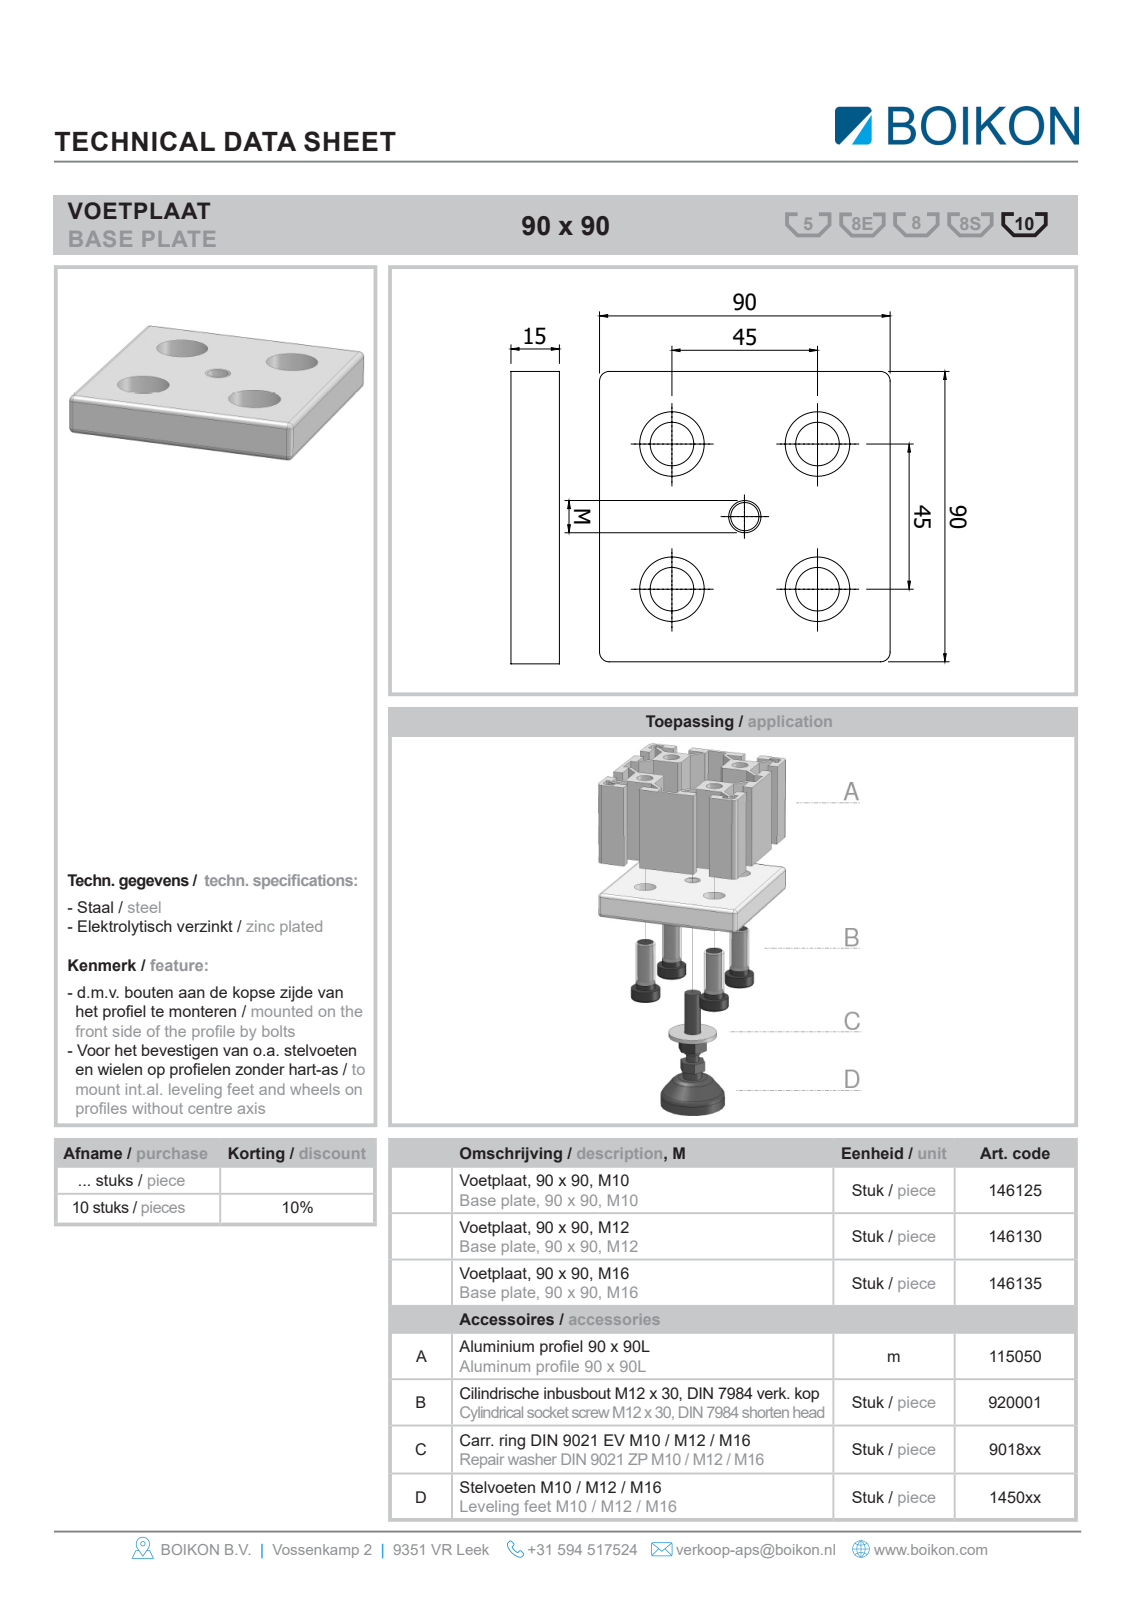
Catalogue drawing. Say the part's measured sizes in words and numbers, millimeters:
The part is named "Root; 146125Voetplaat 90x90 M10BOIKON3*; 920001Cil. inb. M12 x 30, DIN 7984 verk. kopBOIKON0". Its 3-D file was written by "HiCAD 2013 1802.4 Build 509 (AUTOMOTIVE_DESIGN)". It is 5 solids with 107 faces: 74 planar, 21 cylindrical and 12 other. Overall it measures 90 by 90 by 39 millimeters. Its volume is 121 144 cubic millimeters and its surface area 31 853 square millimeters. Round holes: 4 of diameter 13.5, 4 of diameter 20, 1 of diameter 10. Round bosses or shafts: 4 of diameter 18, 4 of diameter 12, 4 of diameter 9.85. The main face-to-face distances are 15, 90, 6, 9, 2, 7, 13, 37, 24, 30. The hole center spacings are 31.82, 45, 63.64.
